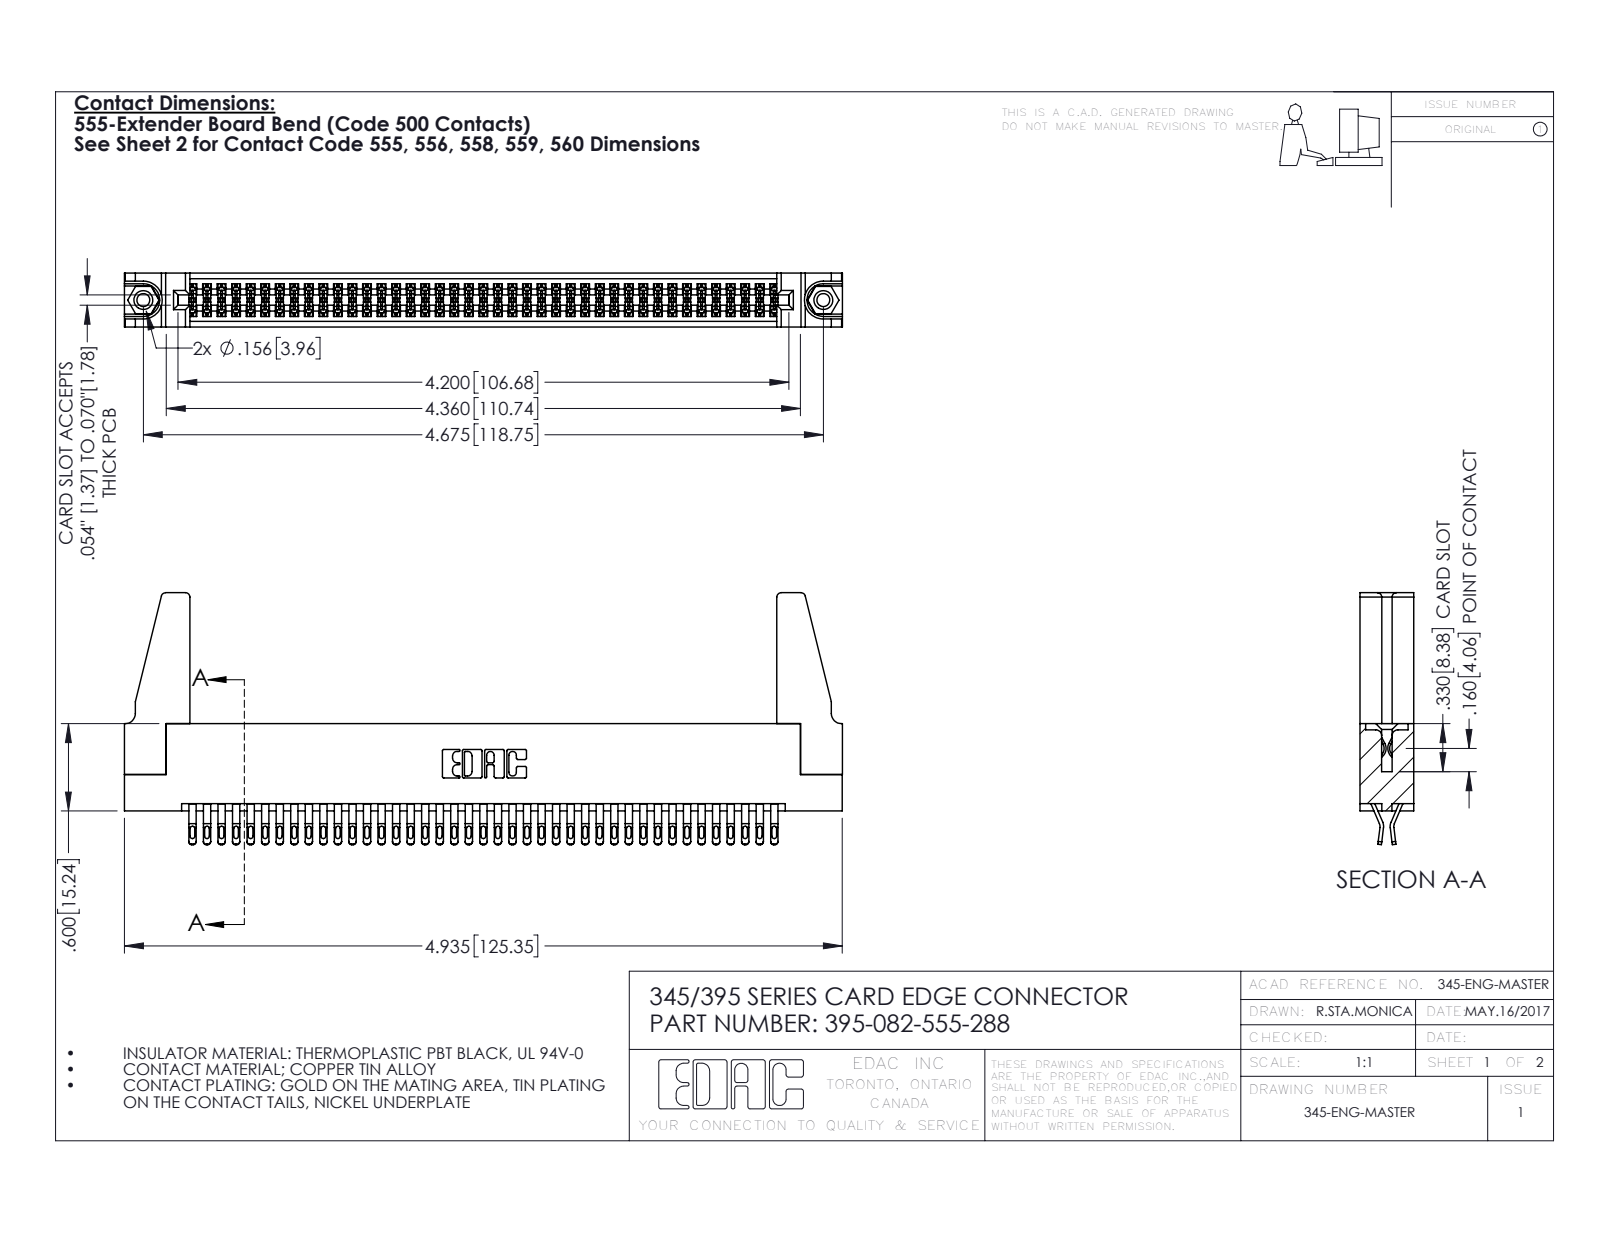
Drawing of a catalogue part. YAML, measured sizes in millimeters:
part_name: "345-250-001_345-250-001-102; 345-292-001_555 Tail; 345 Part_Flush Mounting Lugs - 0.156 Dia-TH; 395-082-555-288 (+1 more)"
step_written_by: "SolidWorks 2016 (CONFIG_CONTROL_DESIGN)"
units: millimeters
bodies: {solids: 87, faces: 4842, planar: 2694, cylindrical: 2132, other: 16}
overall_size: [125.4, 44, 9.4]
volume: 15700
surface_area: 22270
round_holes:
  - {diameter: 2.3, count: 2}
  - {diameter: 3.2, count: 2}
  - {diameter: 4, count: 2}
  - {diameter: 1.6, count: 1}
round_bosses_or_shafts:
  - {diameter: 3.9, count: 2}
partial_cylinders:
  - {radius: 0.4, count: 205}
  - {radius: 0.5, count: 164}
  - {radius: 0.2, count: 123}
  - {radius: 0.3, count: 22}
  - {radius: 0.8, count: 8}
  - {radius: 0.2, count: 6}
  - {radius: 0.8, count: 6}
  - {radius: 0.7, count: 3}
face_to_face_distances: [1.8, 7.6, 9.4, 0.6, 5.1, 2.5, 6.9, 5.7, 4.4, 3.8]
hole_center_spacings: [6.9, 112.8, 118.7]
